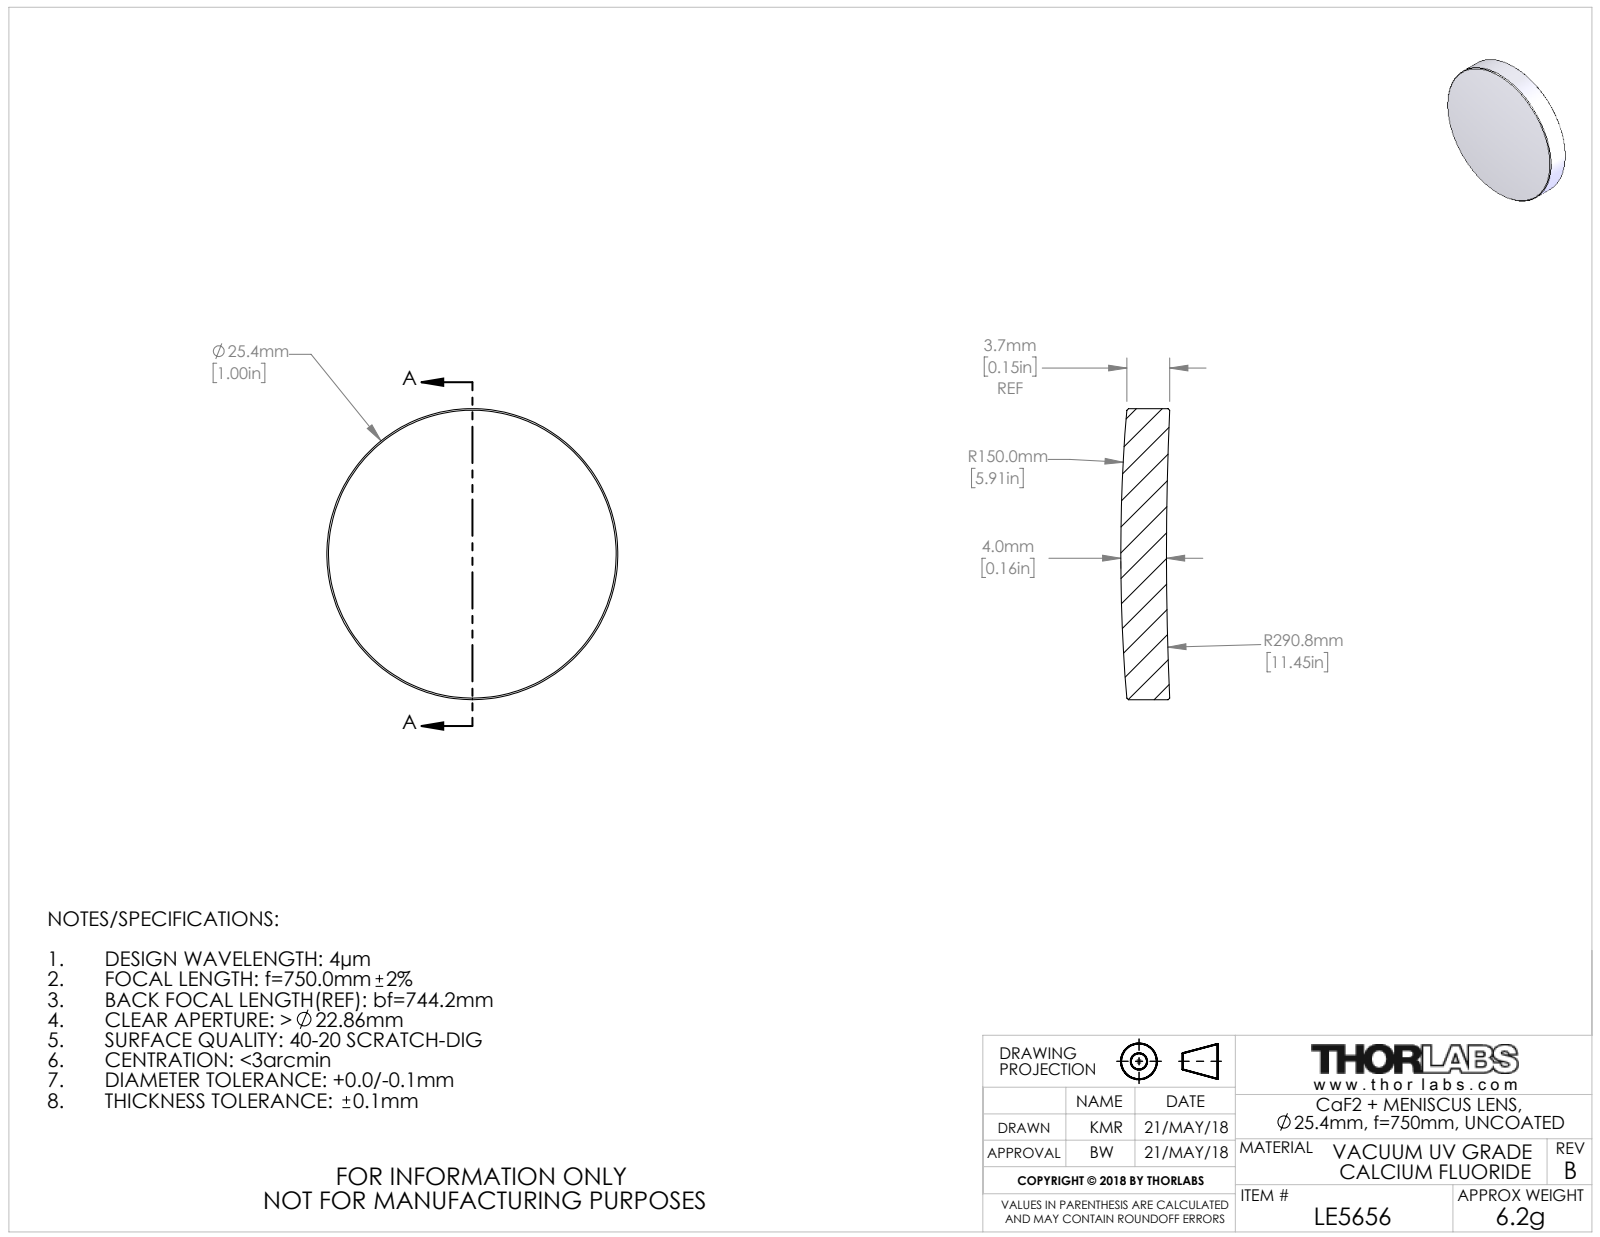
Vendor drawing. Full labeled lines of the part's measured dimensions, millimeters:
Part name (STEP PRODUCT): 21993-E0W
STEP written by: SolidWorks 2016 (CONFIG_CONTROL_DESIGN)
Units: millimetres
Bodies: 1 solid, 10 faces (0 planar, 2 cylindrical, 8 other)
Overall size (bounding box): 25.4 × 25.4 × 4.3
Volume: 1 970 mm³ · Surface area: 1 300 mm²
Round bosses / shafts (diameter × count): ⌀25.4 ×1
